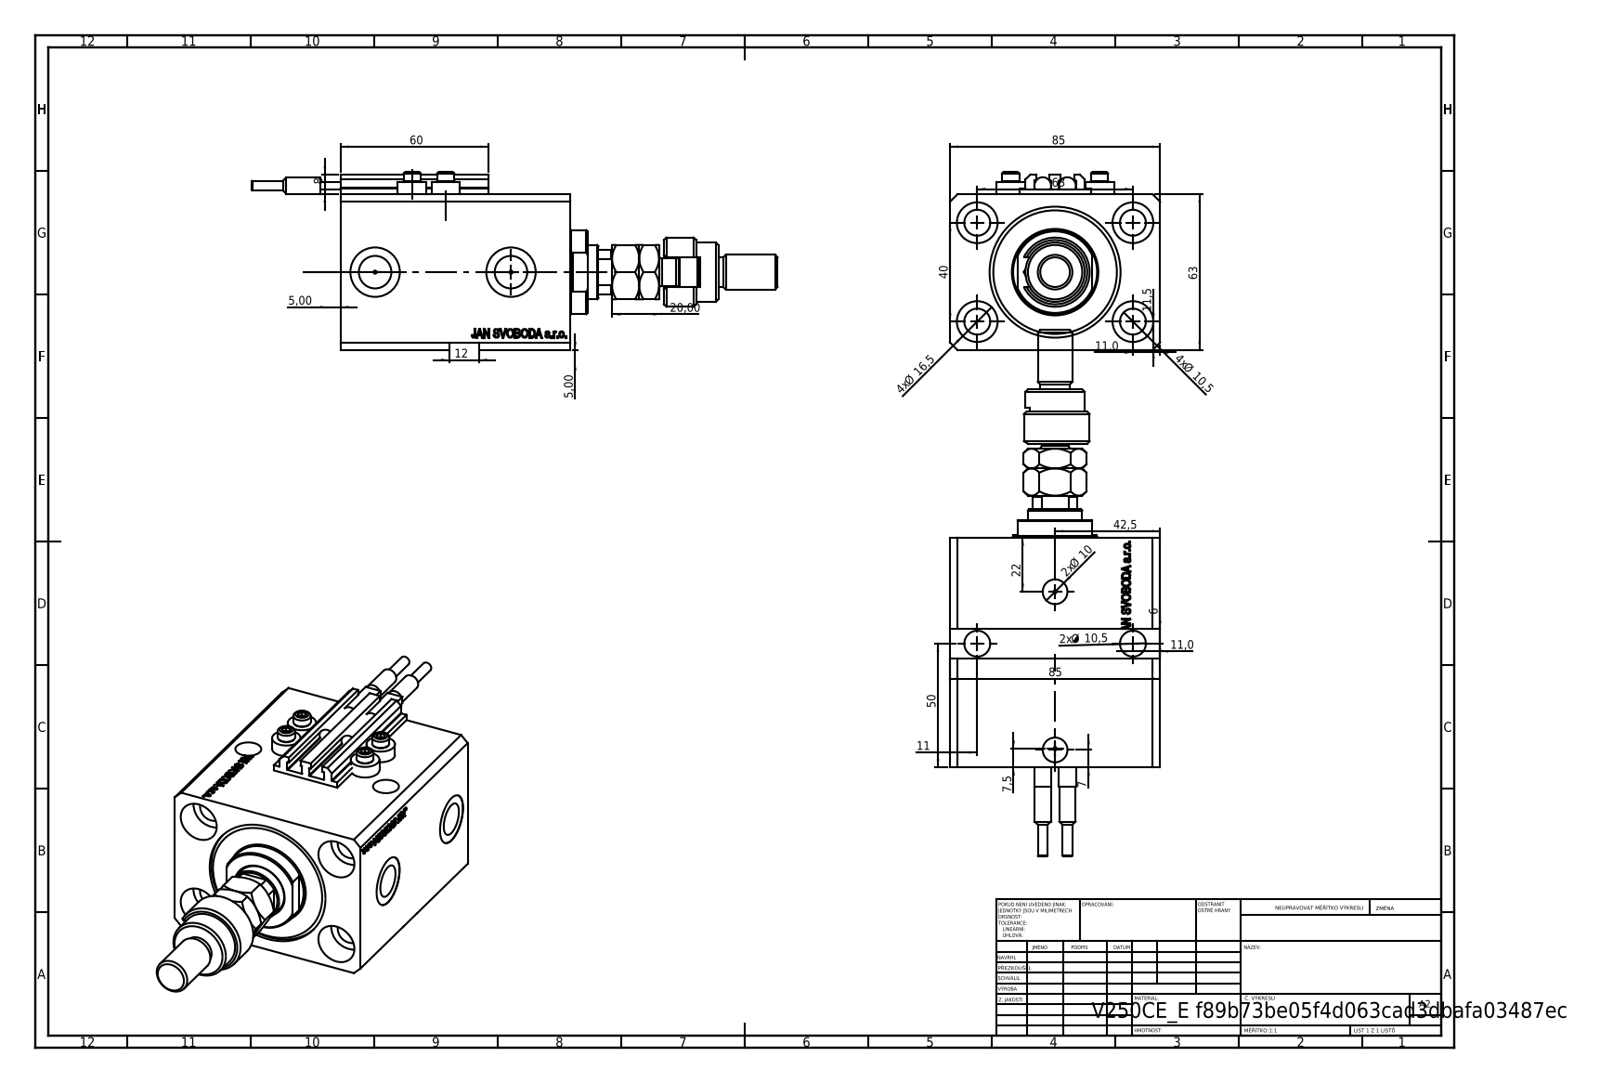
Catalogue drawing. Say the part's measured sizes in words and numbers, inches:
The part is named "ALLEN BOLT V250CE; V250CE_C_VCP; SWITCH_V250CE; V250CE_E_Body (+3 more)". Its 3-D file was written by "SolidWorks 2019 (CONFIG_CONTROL_DESIGN)". It is 12 solids with 1240 faces: 599 planar, 163 cylindrical and 478 other. Overall it measures 8.382 by 3.346 by 2.835 inches. Its volume is 28.02 cubic inches and its surface area 170.2 square inches. Round holes: 6 of diameter 0.413, 4 of diameter 0.049, 4 of diameter 0.157, 4 of diameter 0.65, 2 of diameter 0.394, 2 of diameter 0.518, 2 of diameter 0.787, 1 of diameter 0.492, 1 of diameter 0.866, 1 of diameter 1.575, 1 of diameter 2.087. Round bosses or shafts: 4 of diameter 0.457, 4 of diameter 0.276, 2 of diameter 0.268, 2 of diameter 0.256, 2 of diameter 0.157, 1 of diameter 1.339, 1 of diameter 1.102, 1 of diameter 0.945. Partial cylindrical surfaces (rounded edges, fillets, slot ends): 10 of radius 0.008, 1 of radius 0.384, 1 of radius 0.413. The main face-to-face distances are 2.48, 3.346, 3.661, 2.594, 2.146, 1.067, 0.449, 3.213, 0.118, 2.559. The hole center spacings are 1.469, 2.48, 0.535, 0.606, 0.983, 1.103, 1.119, 1.324.
